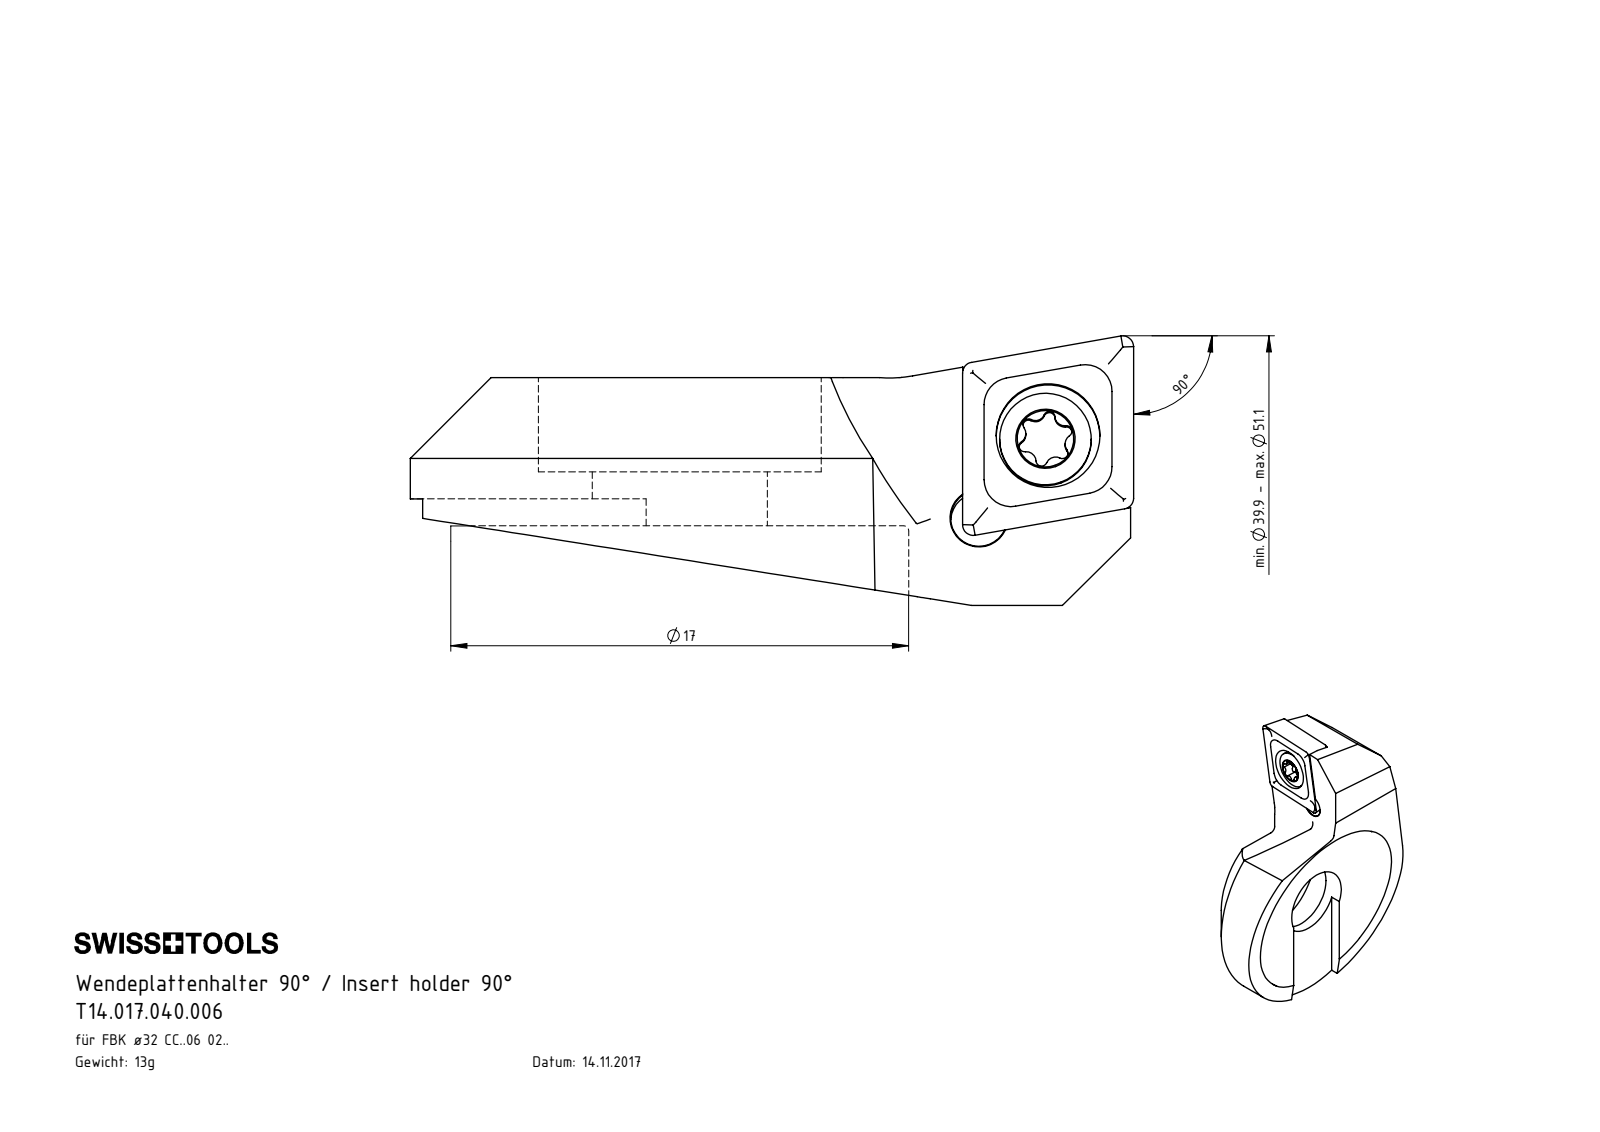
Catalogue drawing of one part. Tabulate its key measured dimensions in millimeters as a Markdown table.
| quantity | value |
| --- | --- |
| part name | WCA-ER2.001.006_A; CCMT060204; F32.WCA.001.007; F32-WCA.001.007_C_fertigbearbeitet |
| STEP written by | SolidWorks 2017 (AUTOMOTIVE_DESIGN) |
| units | millimeters |
| bodies | 3 solids, 103 faces (38 planar, 26 cylindrical, 39 other) |
| overall size | 26.85 × 20 × 10 |
| volume | 1 559 mm³ |
| surface area | 1 544 mm² |
| round holes (diameter × count) | 2.05 × 1, 2.1 × 1, 2.8 × 1, 3.85 × 1, 6.5 × 1, 10.5 × 1 |
| round bosses / shafts (diameter × count) | 3.4 × 1, 2.5 × 1 |
| partial cylindrical surfaces (radius × count) | 0.21 × 6, 0.36 × 5, 0.5 × 2, 0.36 × 1, 5 × 1, 8.5 × 1, 10 × 1, 15 × 1 |
| main face-to-face distances | 1, 5.5, 3.5, 2, 4.5, 2.28, 8.45, 4.95, 3.95, 2.95 |
| hole center spacings | 3.84, 3.99 |
